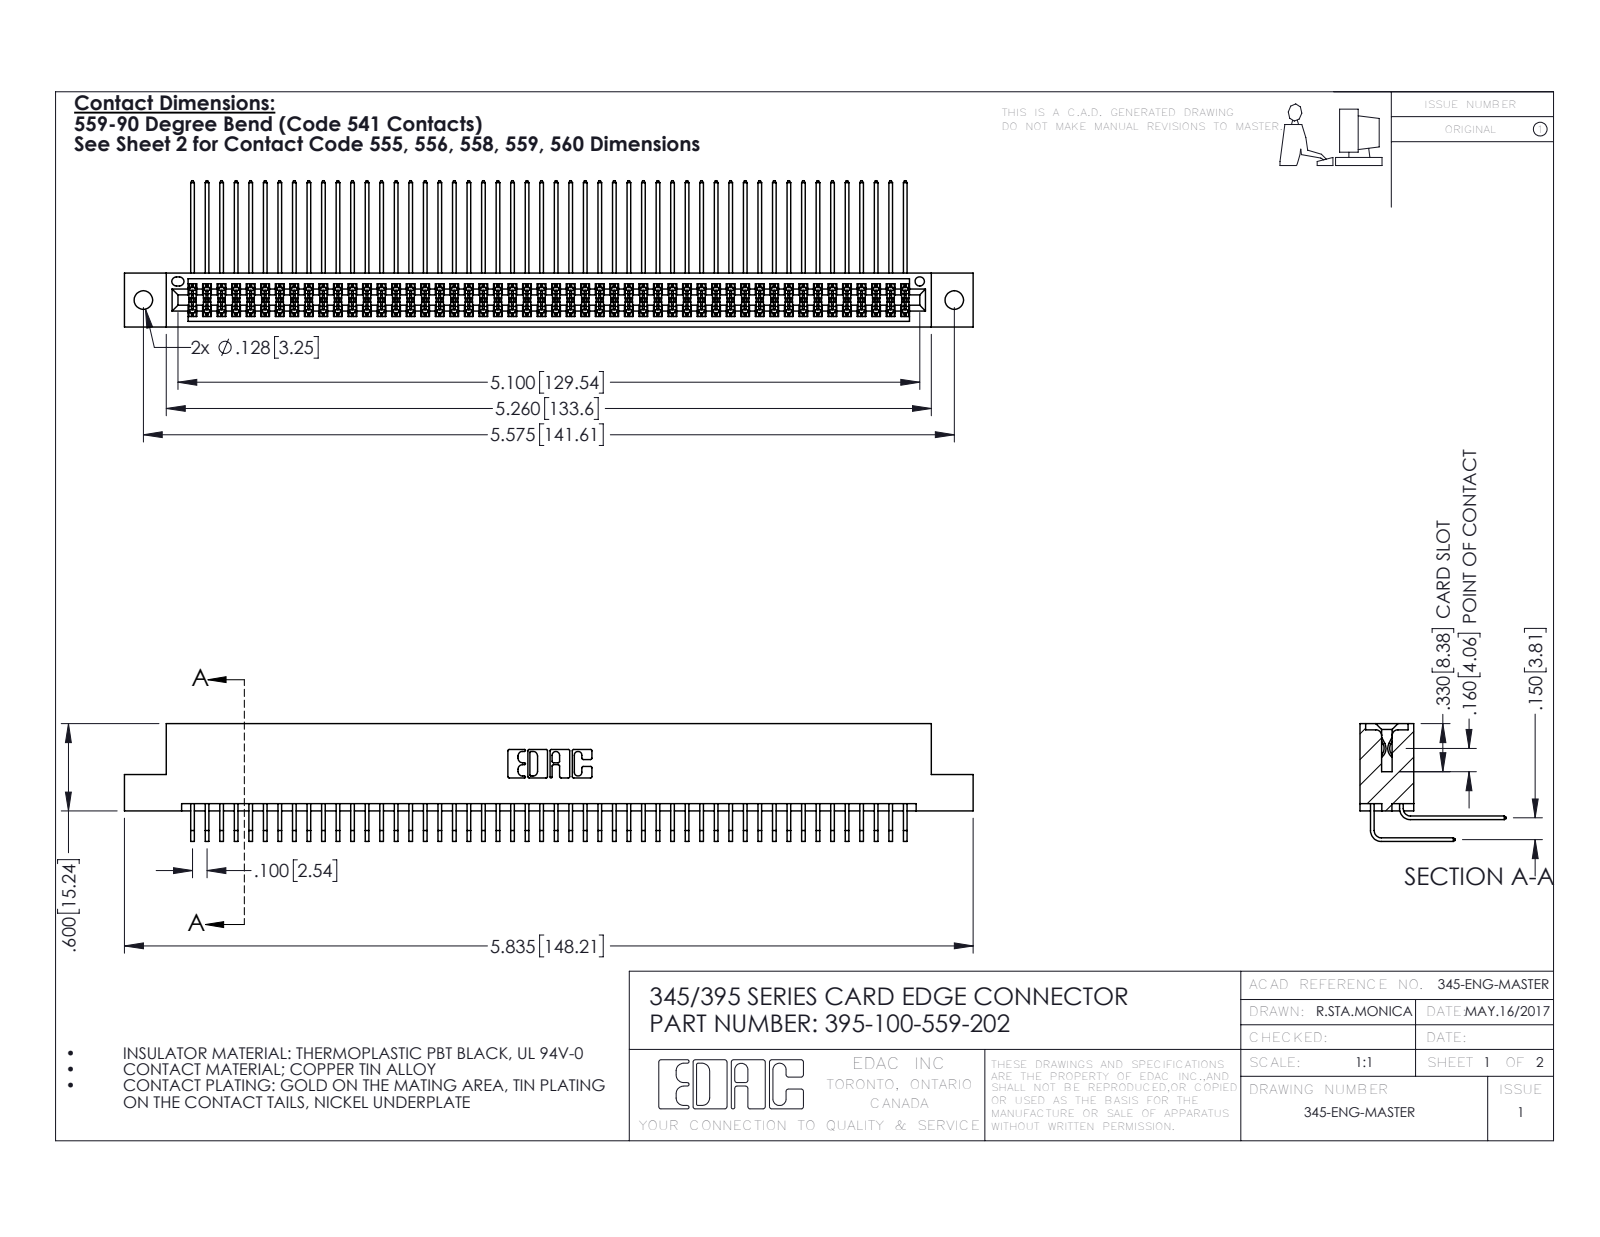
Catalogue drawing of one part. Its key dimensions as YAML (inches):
part_name: "345 Part_Flush Mounting Lugs - 0.128 Dia; 345-292-001_559 Tail - 2; 345-292-001_558 559 Tail - 1; 395-100-559-202"
step_written_by: "SolidWorks 2016 (CONFIG_CONTROL_DESIGN)"
units: inches
bodies: {solids: 101, faces: 5326, planar: 3580, cylindrical: 1746, other: 0}
overall_size: [5.835, 1.005, 0.809]
volume: 0.916
surface_area: 38.42
round_holes:
  - {diameter: 0.128, count: 2}
  - {diameter: 0.064, count: 1}
partial_cylinders:
  - {radius: 0.006, count: 151}
  - {radius: 0.01, count: 22}
  - {radius: 0.007, count: 6}
  - {radius: 0.031, count: 6}
  - {radius: 0.026, count: 3}
  - {radius: 0.014, count: 2}
  - {radius: 0.019, count: 2}
  - {radius: 0.022, count: 2}
face_to_face_distances: [0.072, 0.298, 0.2, 0.37, 0.098, 0.272, 0.025, 0.225, 0.175, 0.15]
hole_center_spacings: [0.27, 5.339, 5.575]
